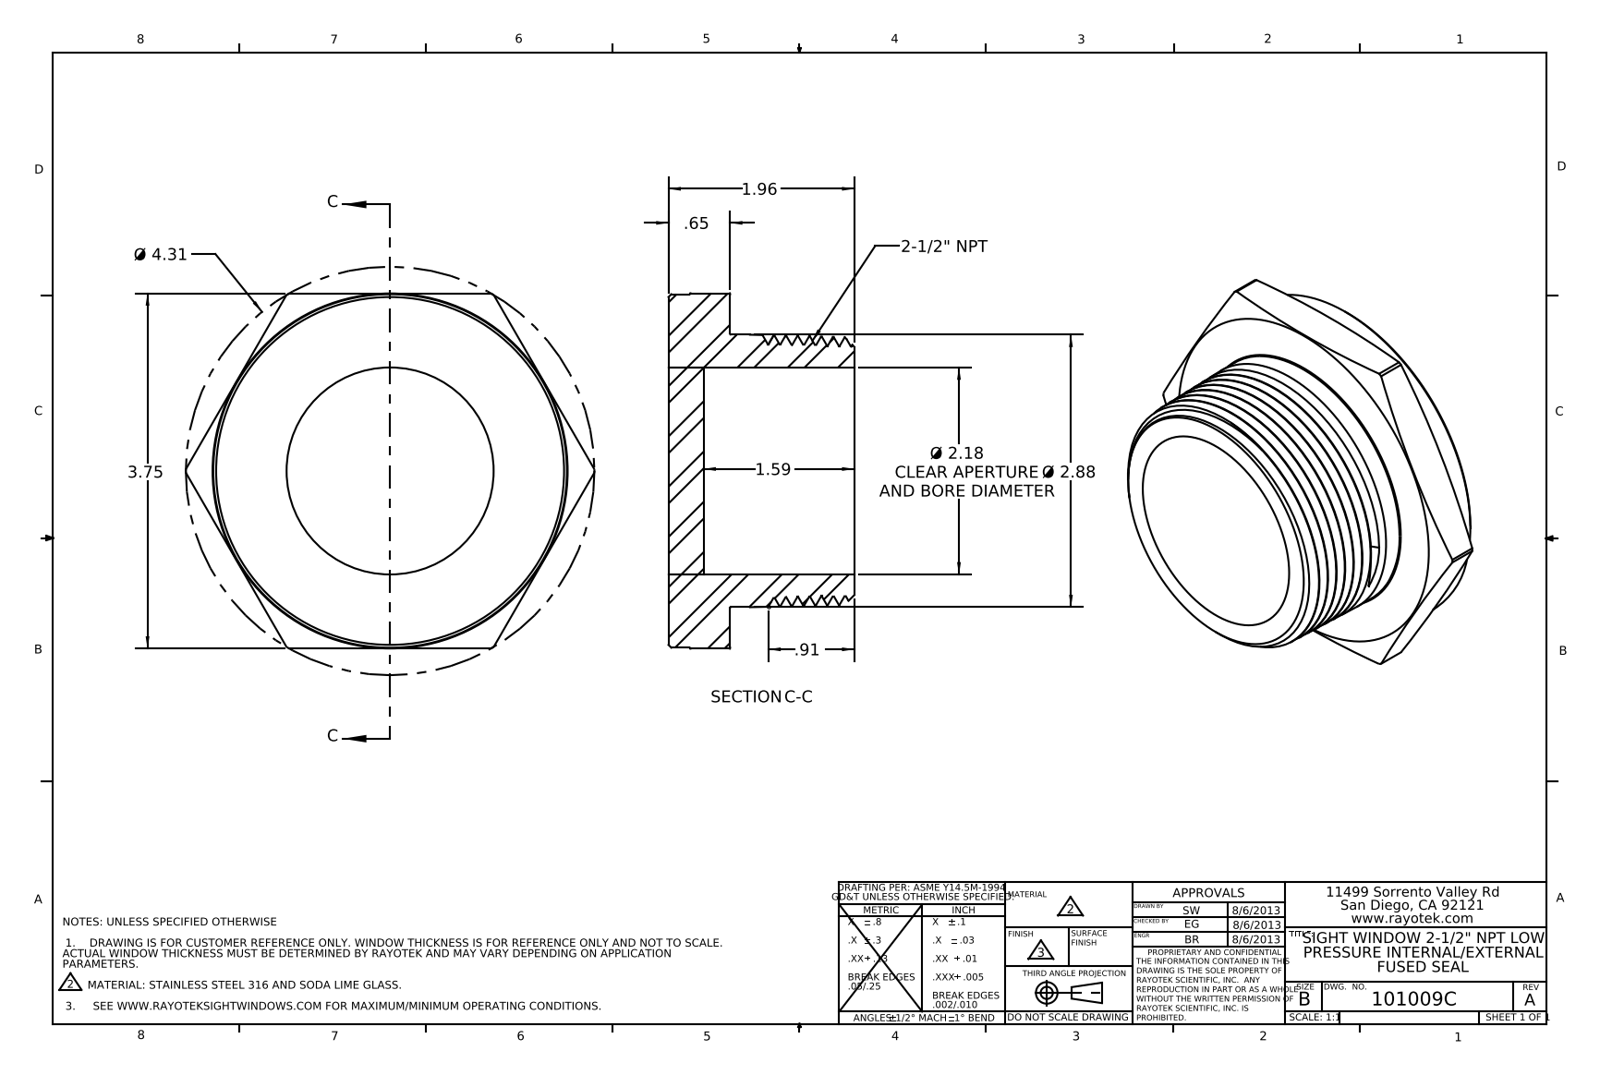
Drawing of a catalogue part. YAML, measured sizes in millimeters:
part_name: "403009"
step_written_by: "SolidWorks 2012 (AUTOMOTIVE_DESIGN)"
units: millimeters
bodies: {solids: 2, faces: 60, planar: 14, cylindrical: 15, other: 31}
overall_size: [109.5, 95.3, 49.8]
volume: 156900
surface_area: 42040
round_holes:
  - {diameter: 55.5, count: 1}
round_bosses_or_shafts:
  - {diameter: 94.7, count: 1}
  - {diameter: 73, count: 1}
partial_cylinders:
  - {radius: 54.7, count: 1}
face_to_face_distances: [16.5, 9.4, 7.1, 95.3, 49.8, 40.4, 33.3]
